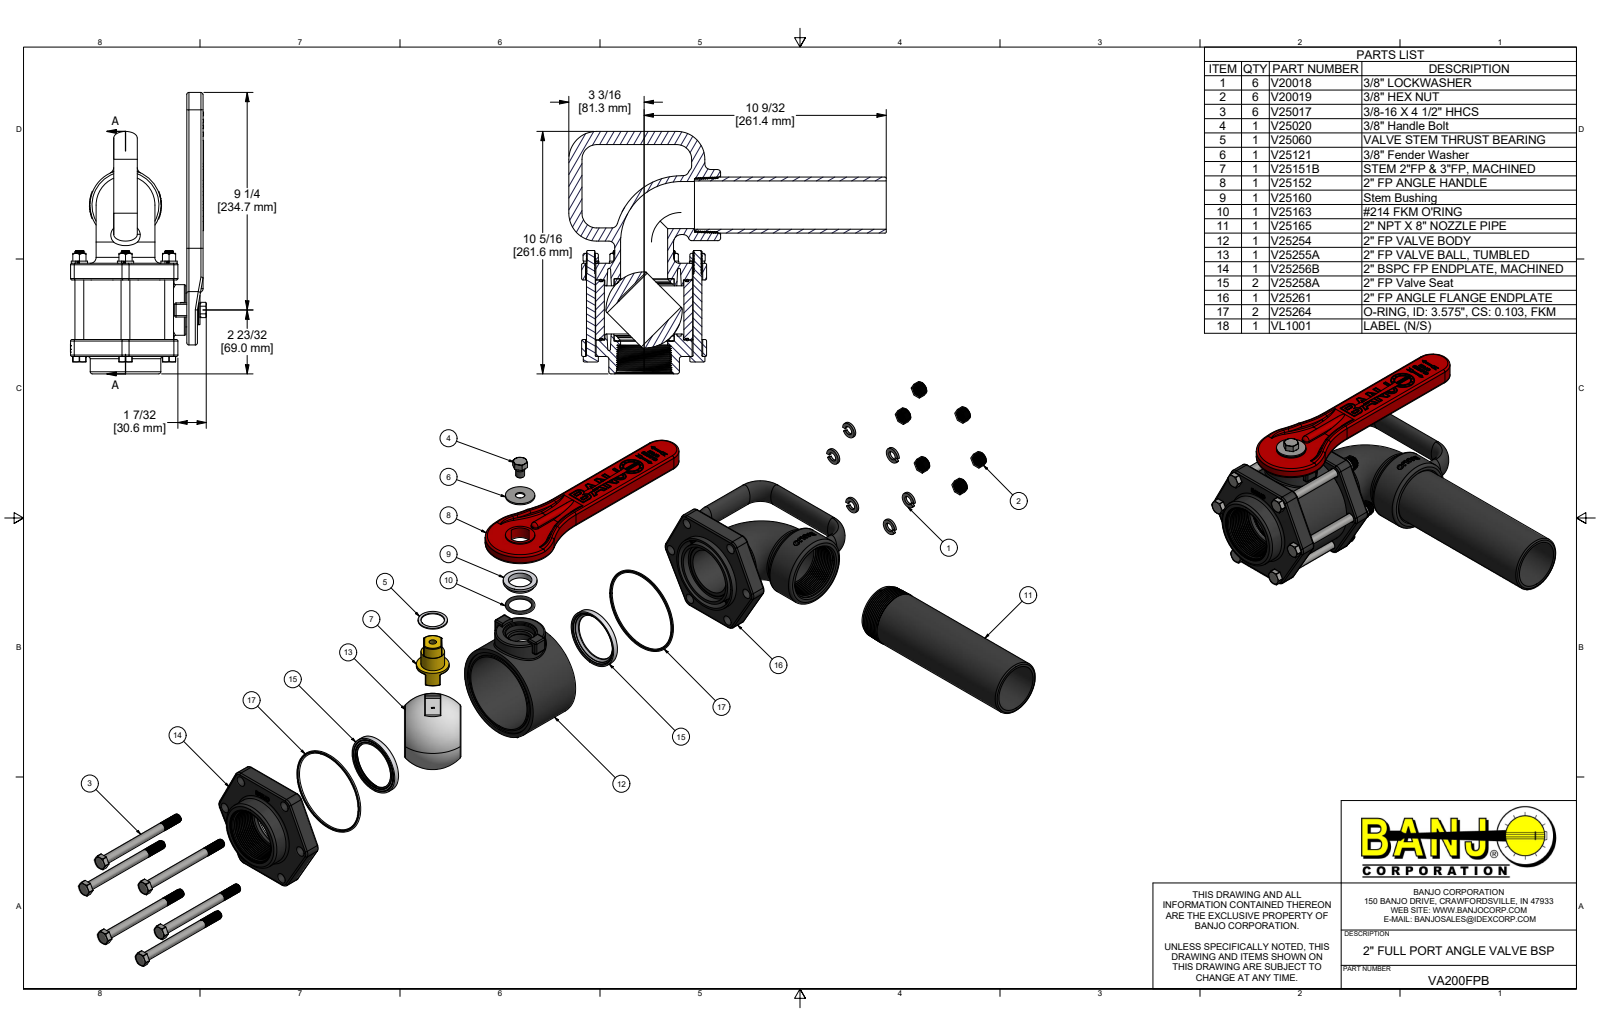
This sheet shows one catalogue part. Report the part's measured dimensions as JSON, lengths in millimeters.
{"part_name": "VA200FPB; V25254; VL1001-D4.125; V20018 (+8 more)", "step_written_by": "Autodesk Inventor 2018 (AUTOMOTIVE_DESIGN)", "units": "millimeters", "bodies": {"solids": 36, "faces": 2957, "planar": 1281, "cylindrical": 638, "other": 1038}, "overall_size": [1153, 303.7, 143.8], "volume_mm3": 1338000, "surface_area_mm2": 771000, "round_holes": [[4.3, 12], [7.8, 6], [9.5, 6], [9.8, 6], [11.2, 6], [11.4, 6], [52.1, 3], [50.8, 2], [7.8, 1], [10.3, 1], [17.3, 1], [24.4, 1]], "round_bosses_or_shafts": [[8.2, 90], [9.5, 7], [17.4, 6], [63.5, 2], [88.9, 1], [84.9, 1], [84.8, 1], [84.7, 1]], "partial_cylinders_radius": [[1.5, 22], [3.2, 13], [0.8, 12], [1.6, 12], [4.1, 12], [8, 12], [0.8, 10], [2.3, 8]], "face_to_face_distances": [18, 82.6, 100.6, 17.8, 64.8, 82.8, 6.6, 16.8, 7.6, 9.9], "hole_center_spacings": [50.2, 71, 97, 26, 87, 41.8, 99.6, 100.4]}
